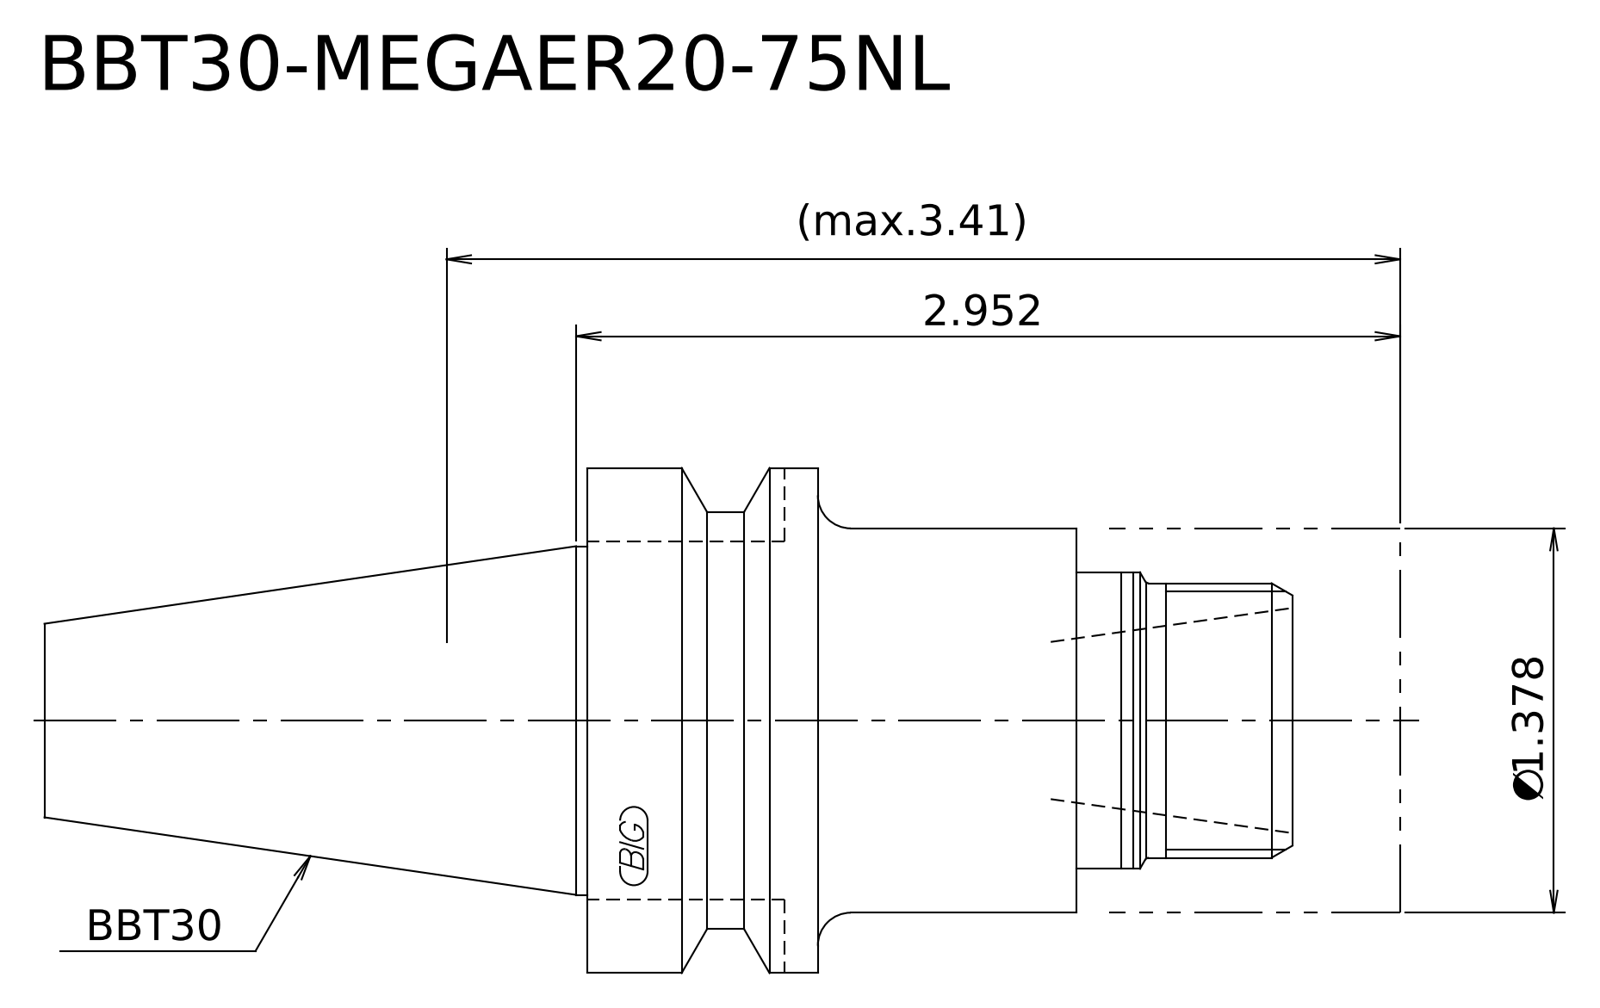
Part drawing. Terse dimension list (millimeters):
written by: Kubotek KeyCreator 2011 V10.0.2 (22737) (automotive_design)
unit: mm
bodies: 2 solids, 21 faces (7 planar, 8 cylindrical, 6 other)
size: 123.4 × 46 × 46
volume: 115 174 mm³; area: 18 896 mm²
bosses: 1× ⌀46, 1× ⌀38, 1× ⌀35, 1× ⌀31.75, 1× ⌀27, 1× ⌀25
face distances: 26.5, 74, 47.5, 9.8, 16.7, 64.2, 29.5, 19.7, 3, 44.5
